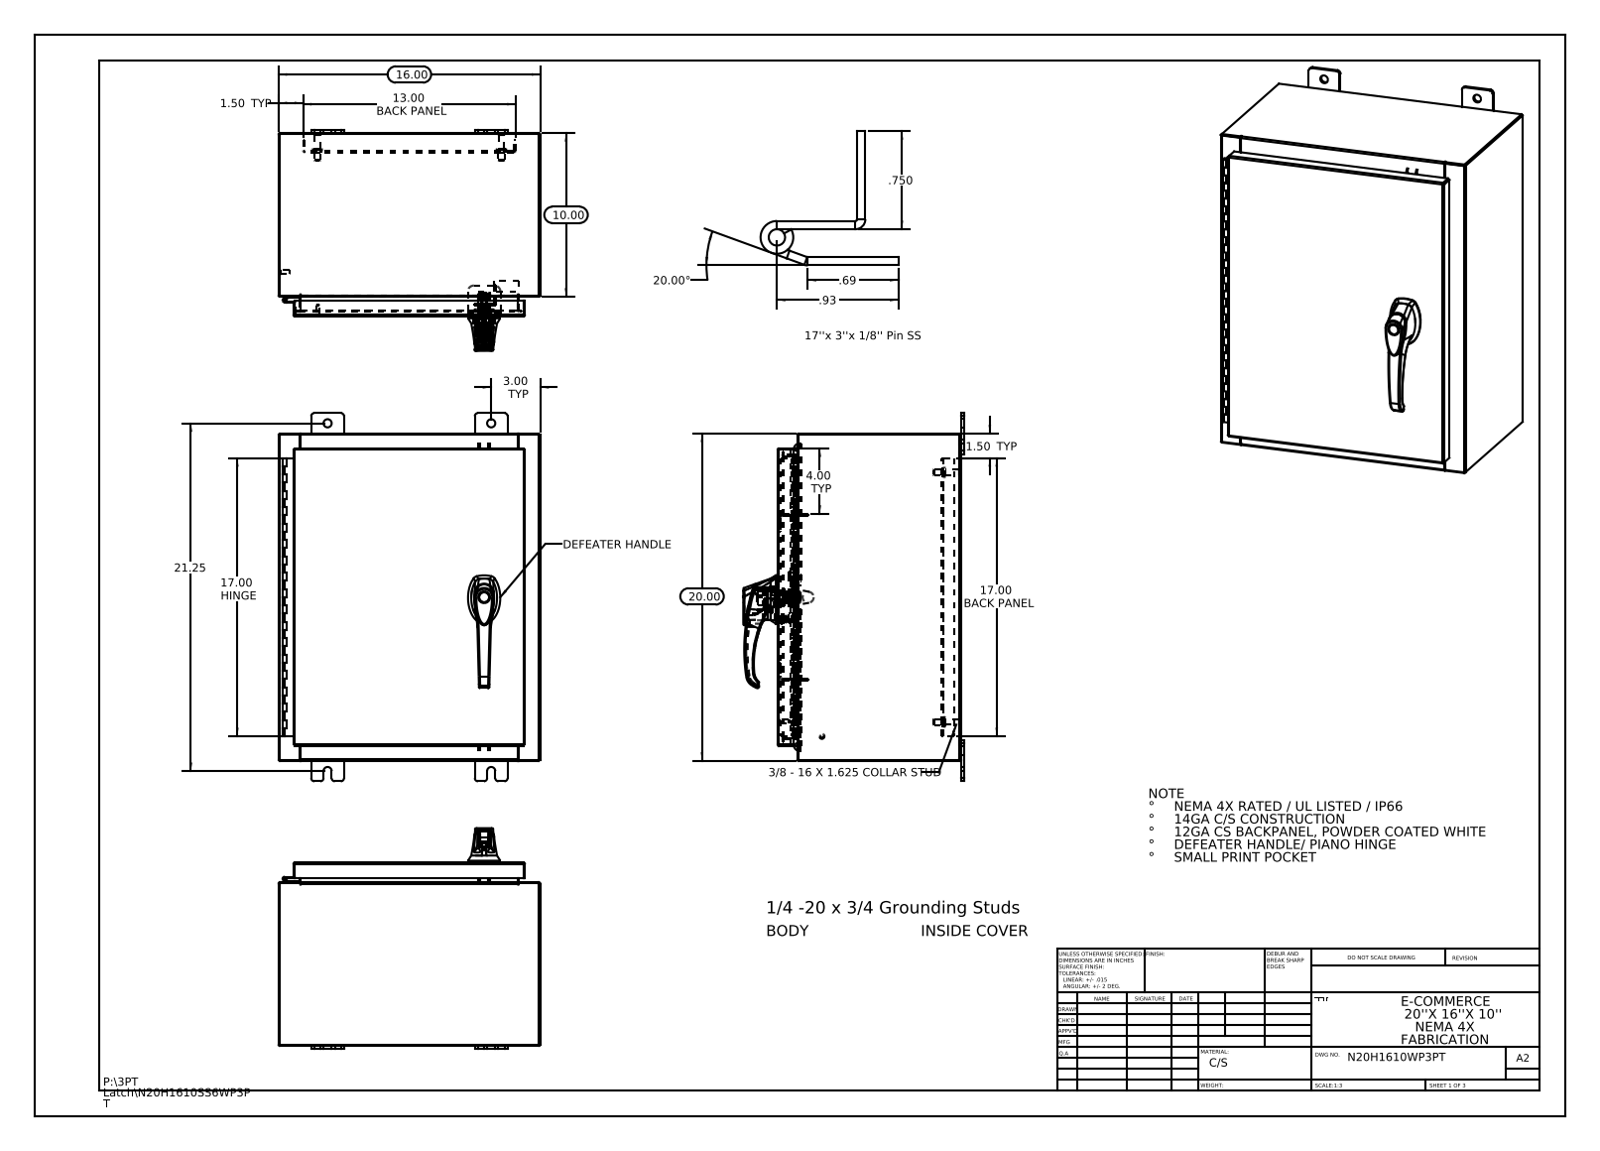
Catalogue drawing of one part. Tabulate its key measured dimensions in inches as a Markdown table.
| quantity | value |
| --- | --- |
| part name | N20H1610SS6WP3PT Cover; 033060_032151; N20H1610SS6WP3PT Hinge Cover Side; N20H1610SS6WP3PT Body (+8 more) |
| STEP written by | SolidWorks 2013 (CONFIG_CONTROL_DESIGN) |
| units | inches |
| bodies | 31 solids, 2316 faces (817 planar, 845 cylindrical, 654 other) |
| overall size | 22.5 × 16 × 13.495 |
| volume | 153.1 in³ |
| surface area | 3 804 in² |
| round holes (diameter × count) | 0.5 × 8, 0.25 × 4, 0.138 × 3, 0.161 × 3, 0.079 × 2, 0.203 × 2, 0.313 × 2, 0.437 × 2, 0.125 × 1, 0.125 × 1, 0.197 × 1, 0.276 × 1 |
| round bosses / shafts (diameter × count) | 0.625 × 4, 0.375 × 4, 0.33 × 4, 1.181 × 1, 0.748 × 1, 0.68 × 1, 0.661 × 1, 0.639 × 1 |
| partial cylindrical surfaces (radius × count) | 0.118 × 37, 0.006 × 33, 0.19 × 24, 0.013 × 22, 0.088 × 18, 0.039 × 15, 0.028 × 12, 0.008 × 6 |
| main face-to-face distances | 0.075, 11.126, 15.925, 19.925, 11.051, 11.201, 0.104, 1, 1.075, 10.051 |
| hole center spacings | 3.404, 11.975, 0.295, 0.625, 0.841, 1.25, 1.313, 1.561 |
